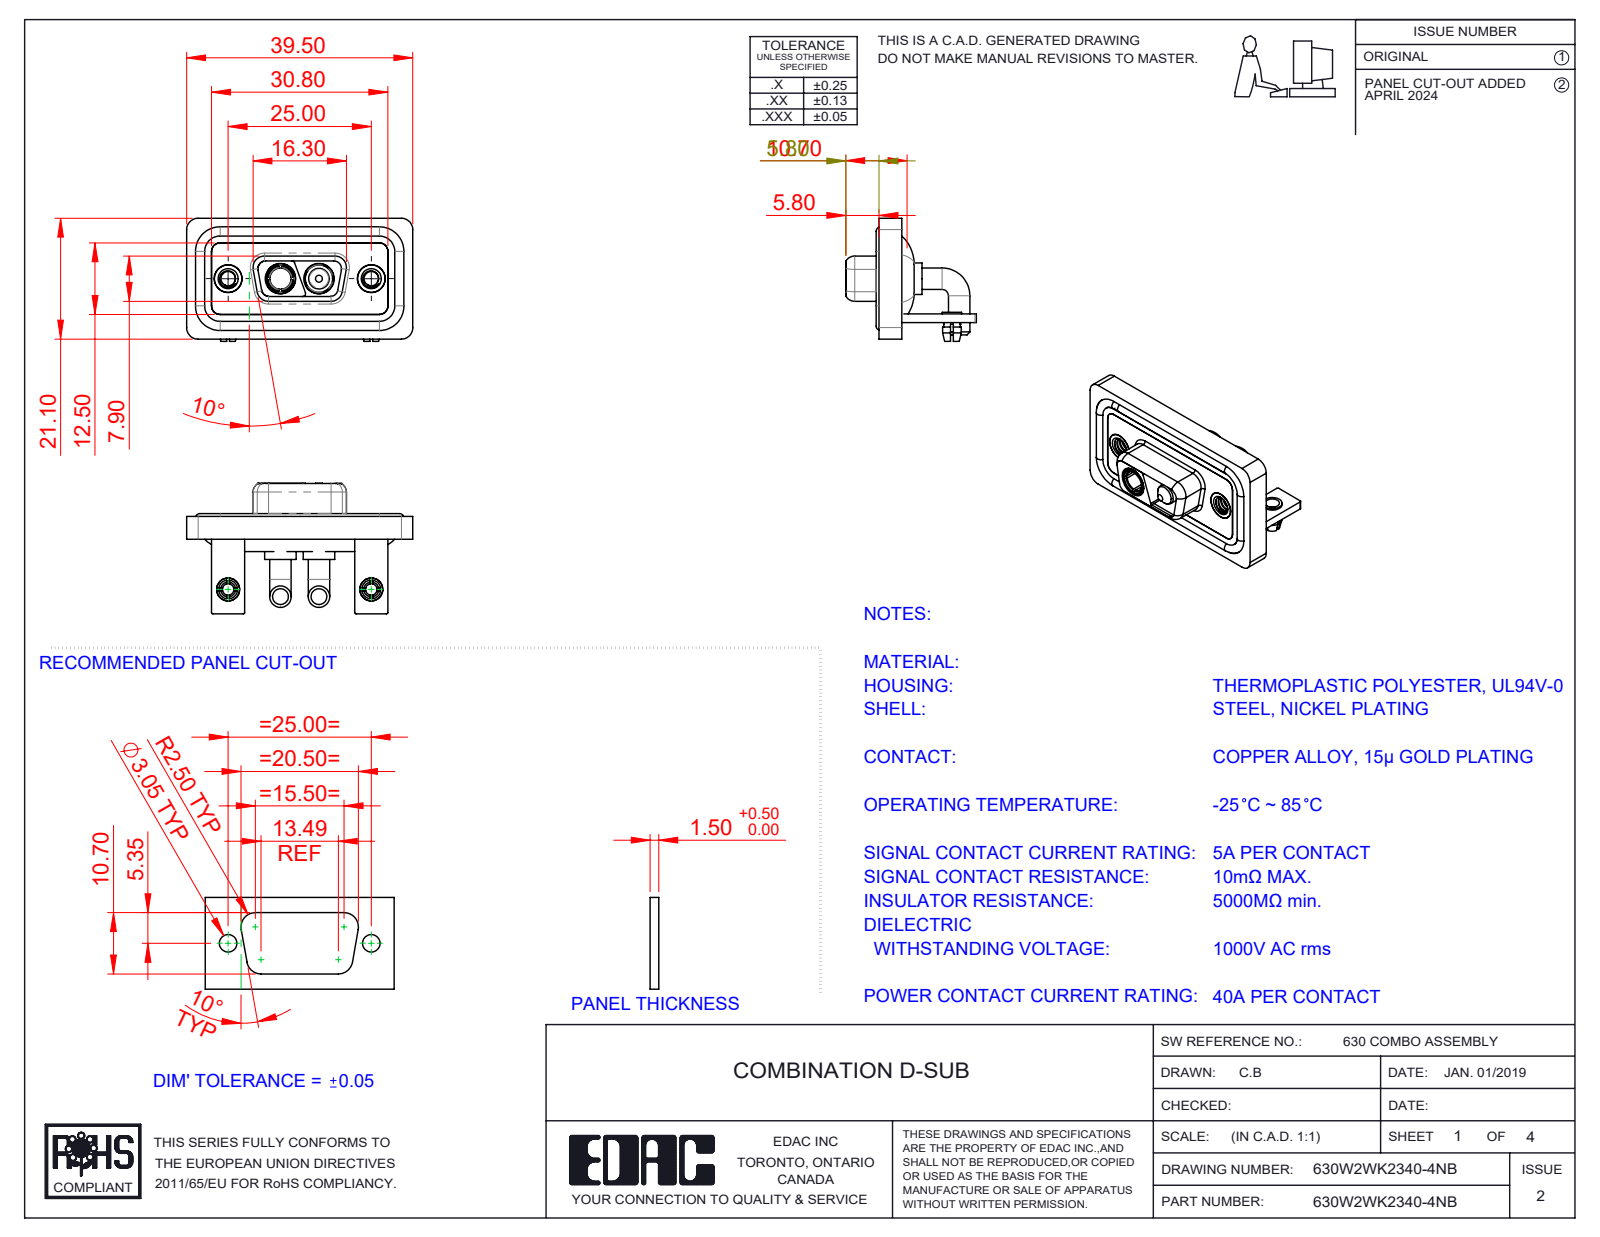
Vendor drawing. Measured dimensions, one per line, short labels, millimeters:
name: 630Combo Shell Rear_09 Contacts; 630Combo Housing_2WK2; 630Combo Waterproof Housing_09 Contacts; Power Pin_40A RA (+6 more)
written by: SolidWorks 2023 (CONFIG_CONTROL_DESIGN)
unit: mm
bodies: 15 solids, 642 faces (212 planar, 289 cylindrical, 141 other)
size: 39.5 × 22.8 × 21.5
volume: 5 248 mm³; area: 8 531 mm²
holes: 4× ⌀2.5, 4× ⌀4.85, 2× ⌀2, 2× ⌀3.2, 2× ⌀4, 2× ⌀4.05, 2× ⌀5, 2× ⌀5.3, 1× ⌀3.7
bosses: 4× ⌀3.75, 4× ⌀1.6, 2× ⌀5.5, 2× ⌀5.2, 2× ⌀4.95, 2× ⌀4.8, 2× ⌀4.75, 2× ⌀4
rounds: 19× R2, 18× R1.5, 16× R0.25, 8× R1.35, 8× R1.6, 7× R0.5, 4× R0.6, 4× R0.65
face distances: 0.4, 2.9, 1.5, 1.1, 3.7, 1.8, 0.8, 2.5, 1.6, 3.1
hole spacings: 9.14, 15.86, 25, 6.72
